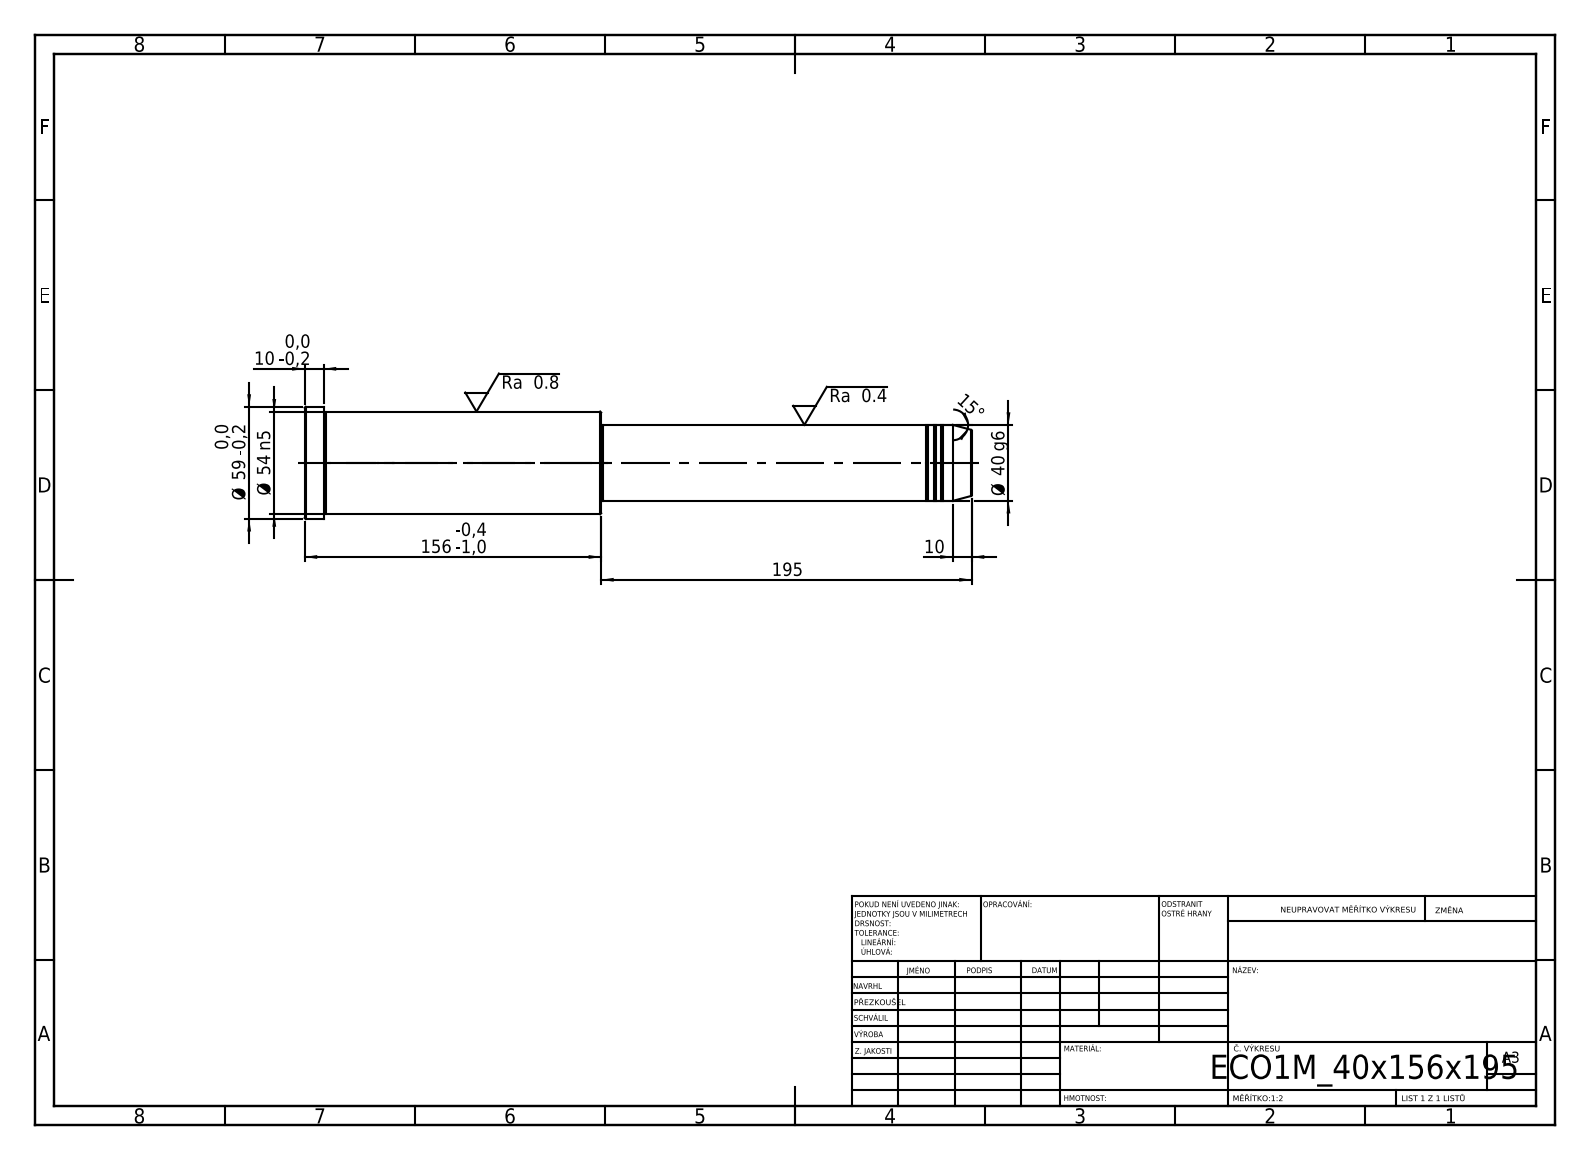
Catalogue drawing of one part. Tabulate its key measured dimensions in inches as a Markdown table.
| quantity | value |
| --- | --- |
| STEP written by | SolidWorks 2019 (CONFIG_CONTROL_DESIGN) |
| units | inches |
| bodies | 1 solid, 43 faces (5 planar, 14 cylindrical, 24 other) |
| overall size | 13.819 × 2.323 × 2.323 |
| volume | 36.91 in³ |
| surface area | 87.64 in² |
| round bosses / shafts (diameter × count) | 2.323 × 1, 2.126 × 1, 1.575 × 1, 1.535 × 1 |
| main face-to-face distances | 6.142, 7.677, 13.819, 13.425, 5.748, 0.394, 7.638, 0.039, 5.787, 6.181 |
